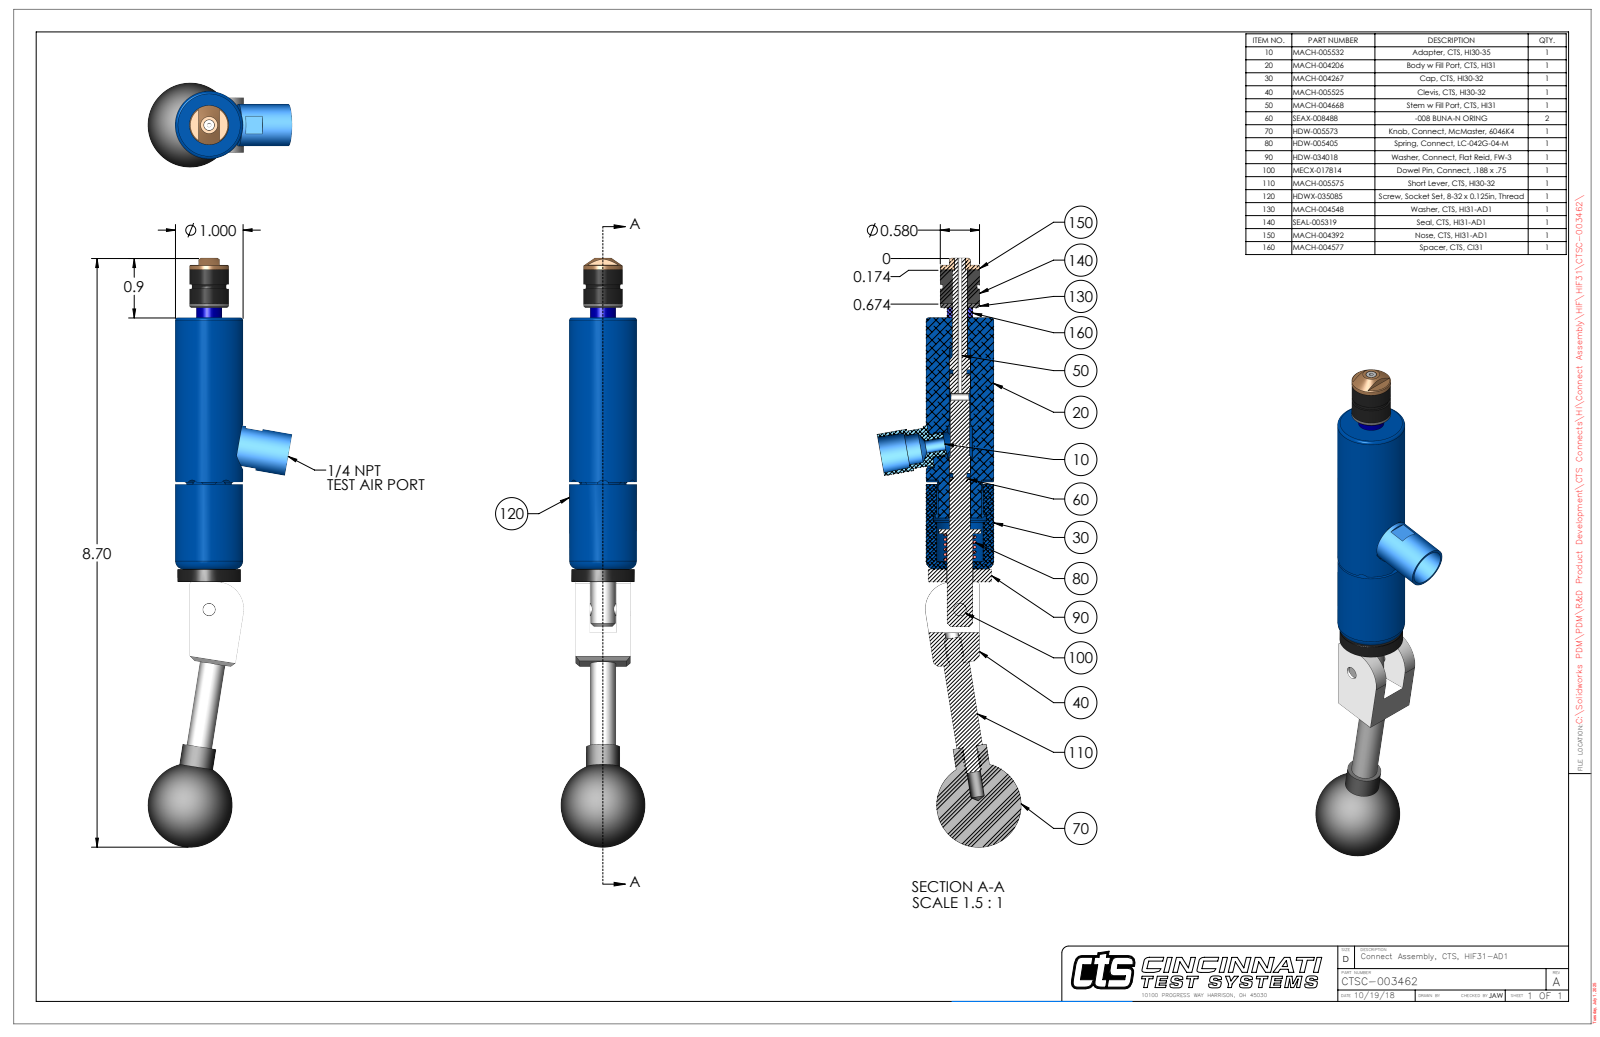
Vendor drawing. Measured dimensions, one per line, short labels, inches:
name: CTSC-003462
written by: SolidWorks 2023 (AUTOMOTIVE_DESIGN)
unit: in
bodies: 10 solids, 293 faces (106 planar, 121 cylindrical, 66 other)
size: 8.704 × 2.128 × 1.25
volume: 5.052 in³; area: 39.08 in²
holes: 2× ⌀0.201, 1× ⌀0.063, 1× ⌀0.109, 1× ⌀0.136, 1× ⌀0.15, 1× ⌀0.159, 1× ⌀0.187, 1× ⌀0.189, 1× ⌀0.218, 1× ⌀0.228, 1× ⌀0.229, 1× ⌀0.385
bosses: 1× ⌀1, 1× ⌀0.936, 1× ⌀0.62, 1× ⌀0.58, 1× ⌀0.5, 1× ⌀0.38, 1× ⌀0.379, 1× ⌀0.375
rounds: 6× R0.093, 2× R0.029, 1× R0.059, 1× R0.325, 1× R0.4, 1× R0.448
face distances: 0.21, 0.602, 0.812, 0.187, 3.716, 3.903, 0.391, 0.705, 4.42, 4.608
hole spacings: 0.599, 1.658, 2.252
